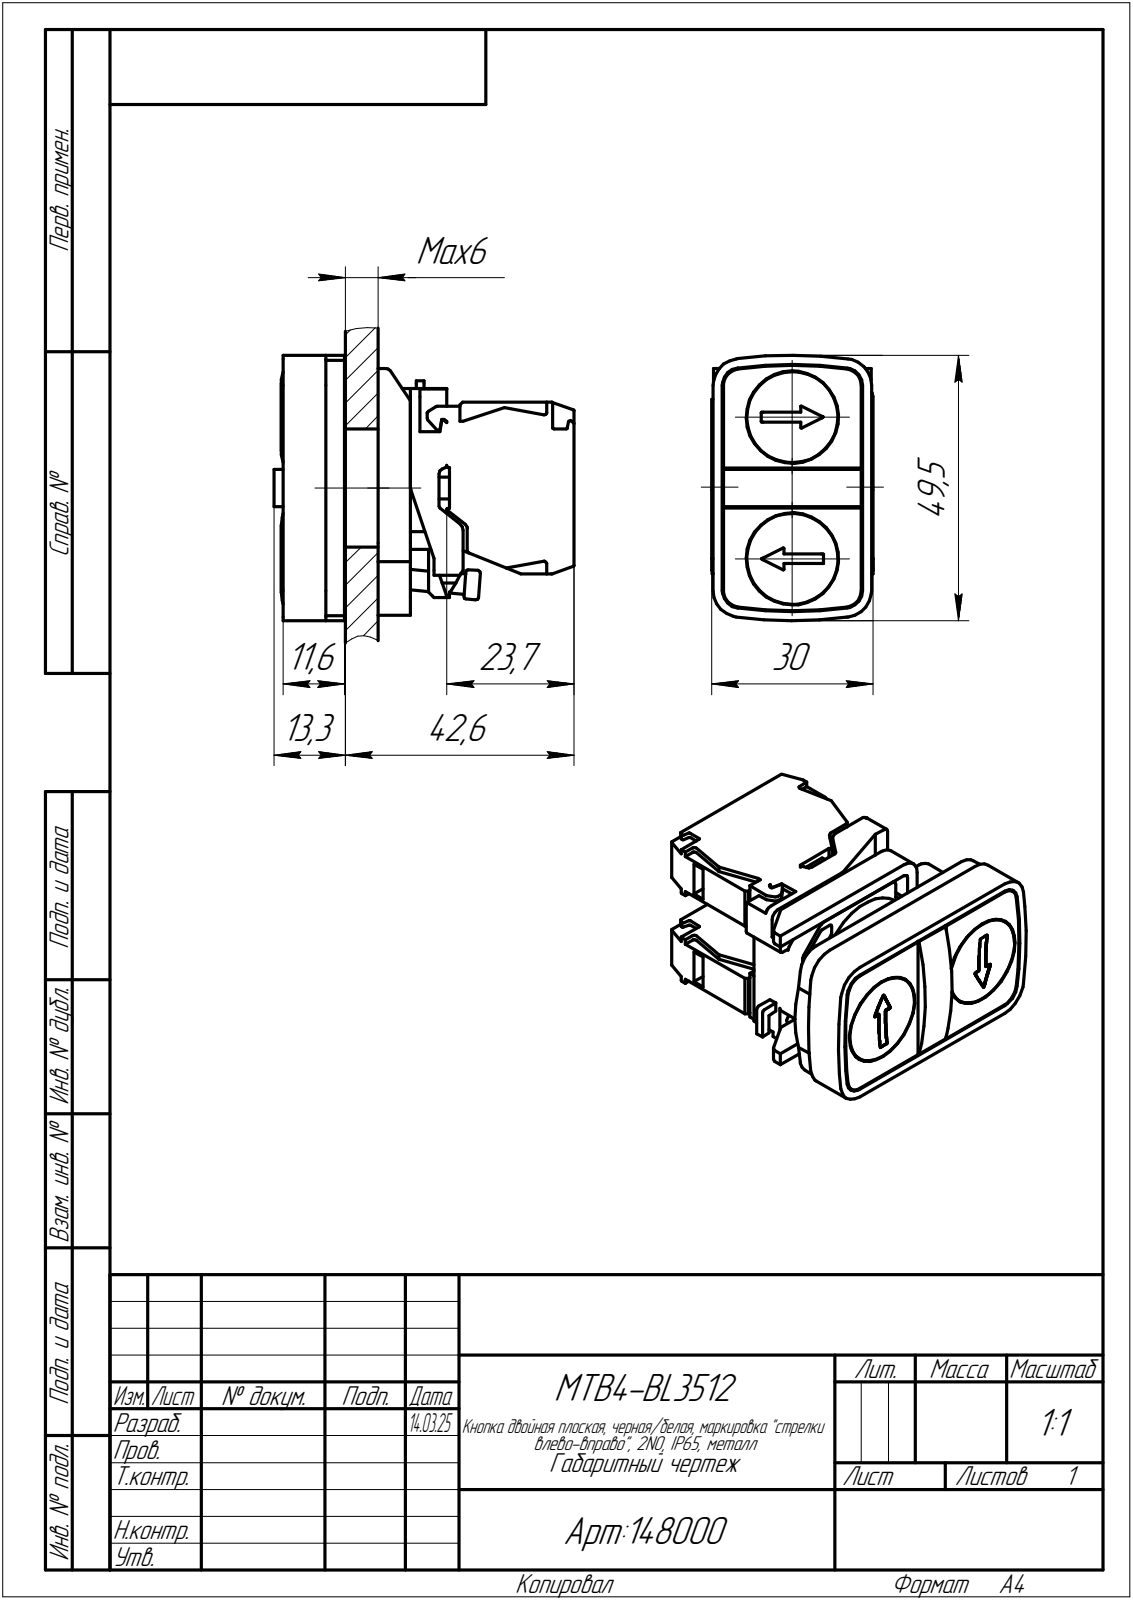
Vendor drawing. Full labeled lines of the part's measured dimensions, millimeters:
Part name (STEP PRODUCT): MTB4-BL3512
STEP written by: C3D Toolkit (CONFIG_CONTROL_DESIGN)
Units: millimetres
Bodies: 2 solids, 537 faces (340 planar, 167 cylindrical, 30 other)
Overall size (bounding box): 55.9 × 49.5 × 30
Volume: 41 978 mm³ · Surface area: 17 972 mm²
Round holes (diameter × count): ⌀1.5 ×2, ⌀17.2 ×2, ⌀20.5 ×1
Round bosses / shafts (diameter × count): ⌀17 ×2, ⌀26.8 ×1, ⌀22 ×1, ⌀5.5 ×1, ⌀3.8 ×1
Partial cylindrical surfaces — rounded edges, fillets, slot ends (radius × count): R0.5 ×23, R0.1 ×10, R0.2 ×10, R0.8 ×7, R1 ×5, R1.02 ×4, R3.1 ×4, R3.3 ×4
Main face-to-face distances: 20, 9.9, 11.4, 2.5, 29.9, 10.1, 1.95, 1.82, 29.75, 17.7
Hole centre spacings: 13.2, 11.56, 11.88, 17.84, 19.73, 23.22, 26.4, 29.18
